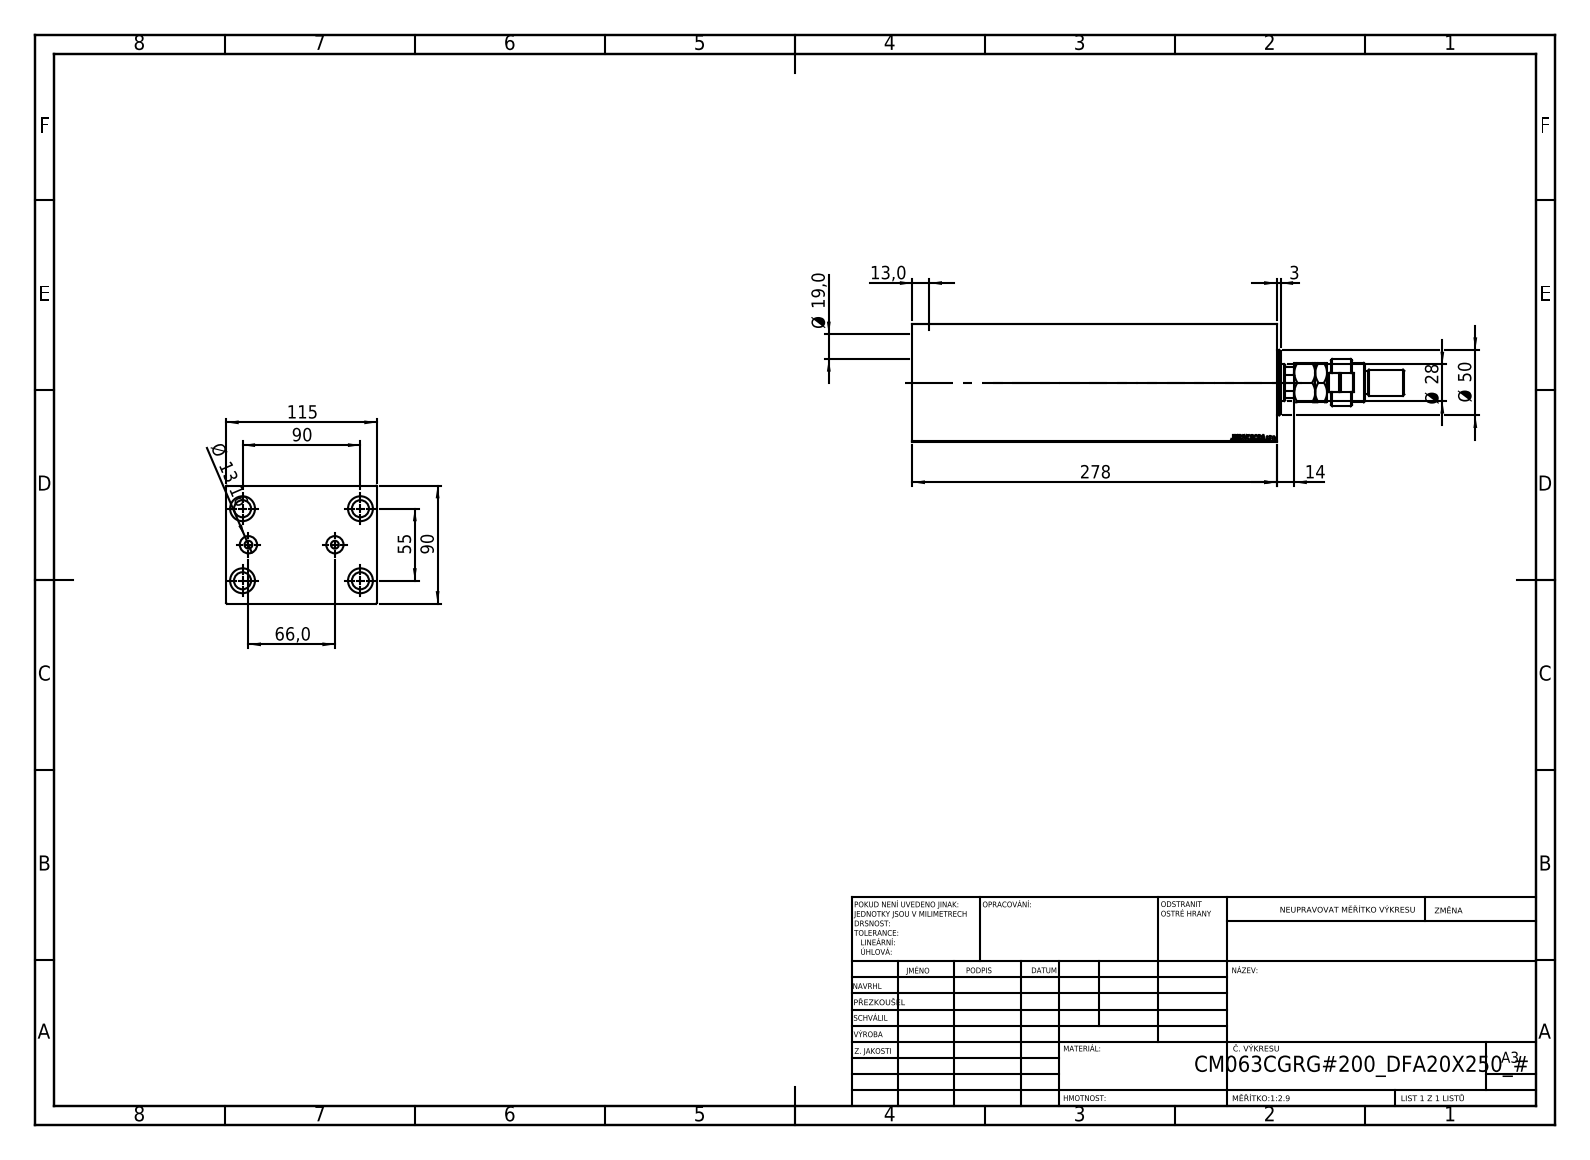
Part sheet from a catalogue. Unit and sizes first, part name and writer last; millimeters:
Units: millimetres
Overall size (bounding box): 375.5 × 115 × 90
Round holes (diameter × count): ⌀13 ×4, ⌀19 ×4, ⌀6 ×2, ⌀13.16 ×2, ⌀18.5 ×1, ⌀28 ×1, ⌀31.5 ×1, ⌀63 ×1, ⌀65 ×1, ⌀72 ×1
Round bosses / shafts (diameter × count): ⌀50 ×1, ⌀36 ×1, ⌀30 ×1, ⌀22 ×1, ⌀20 ×1, ⌀18 ×1, ⌀14 ×1
Partial cylindrical surfaces — rounded edges, fillets, slot ends (radius × count): R7.5 ×1, R12 ×1, R13.5 ×1
Main face-to-face distances: 90, 115, 278, 17.5, 260.5, 13.5, 247, 264.5, 64.5, 47
Hole centre spacings: 52.74, 27.87, 33.71, 55, 75.67, 89.81, 90, 105.48
Volume: 2 256 000 mm³ · Surface area: 300 100 mm²
Bodies: 5 solids, 945 faces (436 planar, 71 cylindrical, 438 other)
Part name (STEP PRODUCT): V450CM_VC_B; FEMALE_PART_FOR_DFA; V450CM_C_Body; V450CM_C_VCP (+1 more)
STEP written by: SolidWorks 2019 (CONFIG_CONTROL_DESIGN)
